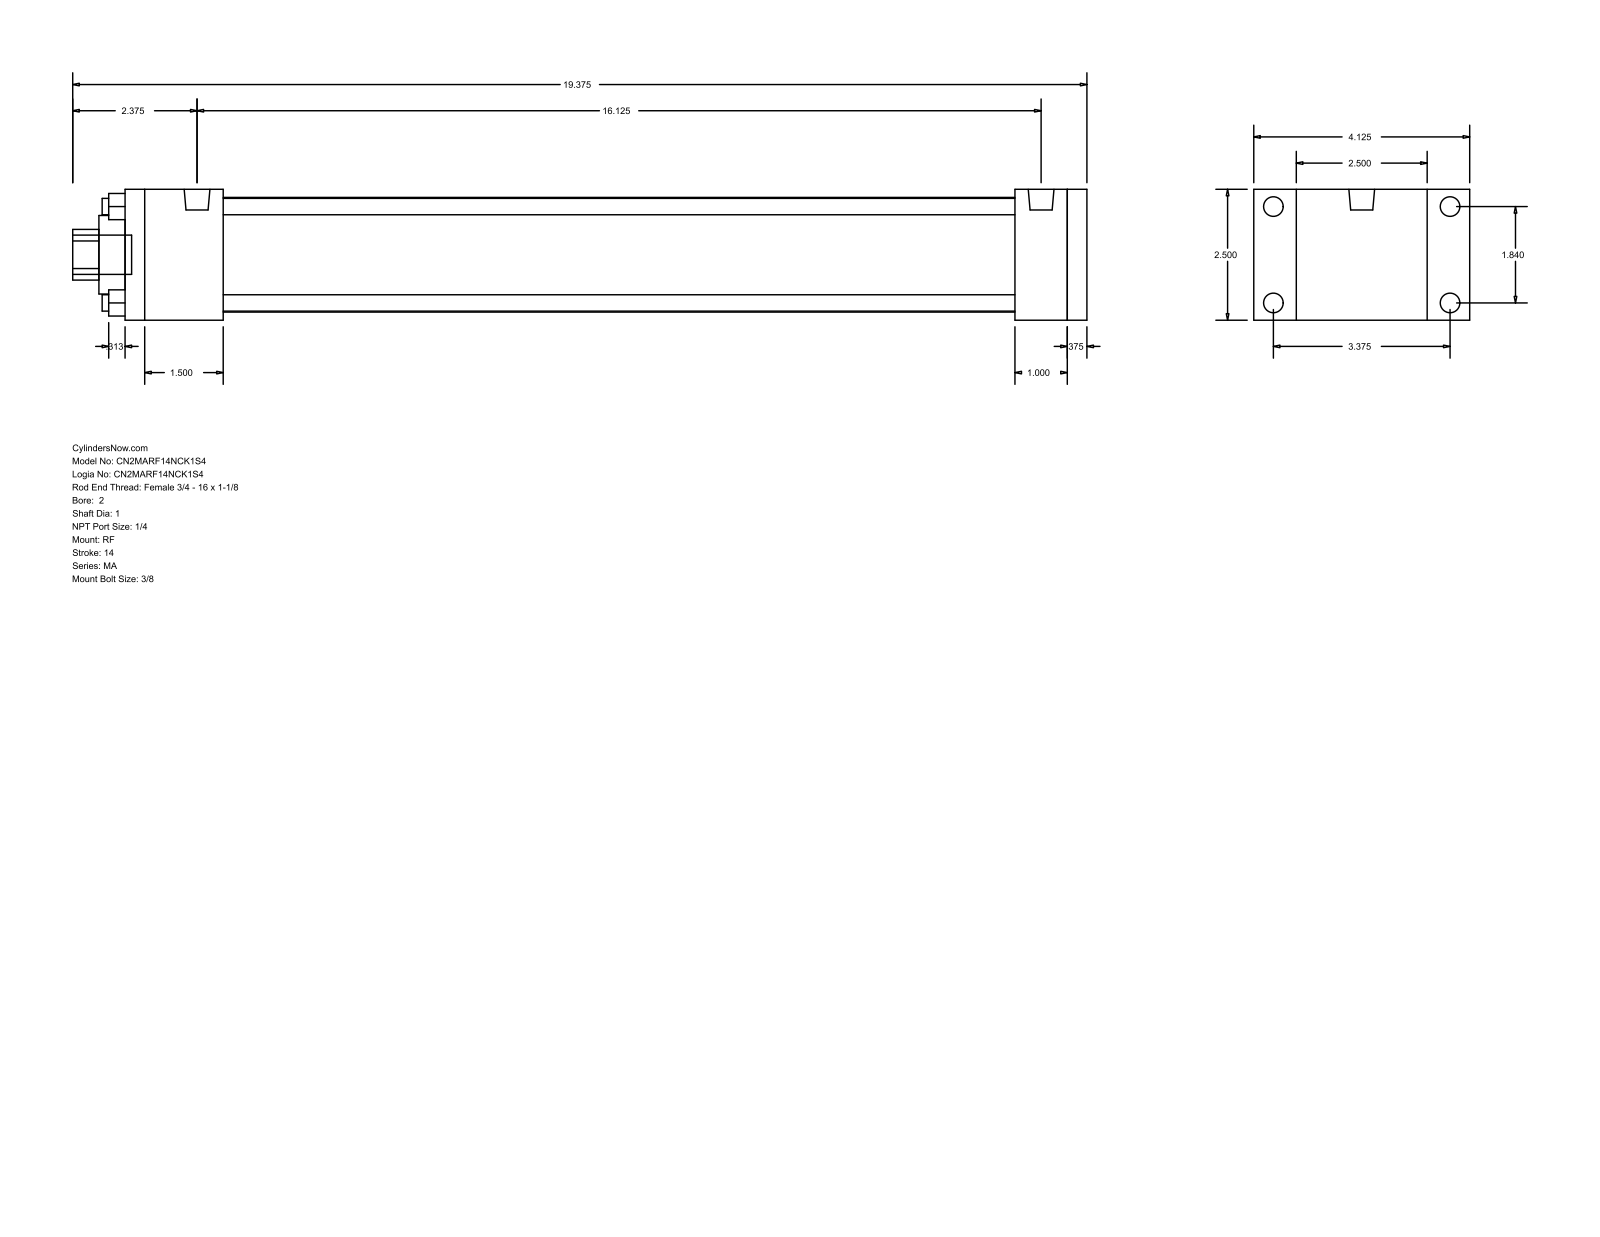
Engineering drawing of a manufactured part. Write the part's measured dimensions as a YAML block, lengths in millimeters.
part_name: "MA_RF__0200_1"
step_written_by: "GSSL Pune (CONFIG_CONTROL_DESIGN)"
units: millimeters
bodies: {solids: 0, faces: 92, planar: 64, cylindrical: 28, other: 0}
overall_size: [492.12, 104.78, 63.5]
round_holes:
  - {diameter: 7.94, count: 4}
  - {diameter: 25.4, count: 1}
  - {diameter: 38.1, count: 1}
  - {diameter: 55.63, count: 1}
round_bosses_or_shafts:
  - {diameter: 9.53, count: 4}
  - {diameter: 7.94, count: 4}
  - {diameter: 12.49, count: 2}
  - {diameter: 19.05, count: 1}
partial_cylinders:
  - {radius: 12.29, count: 1}
face_to_face_distances: [63.5, 457.2, 9.52, 466.72, 25.4, 20.64, 12.7, 47.63, 409.57, 419.09]
hole_center_spacings: [33.05, 46.74, 66.1]
